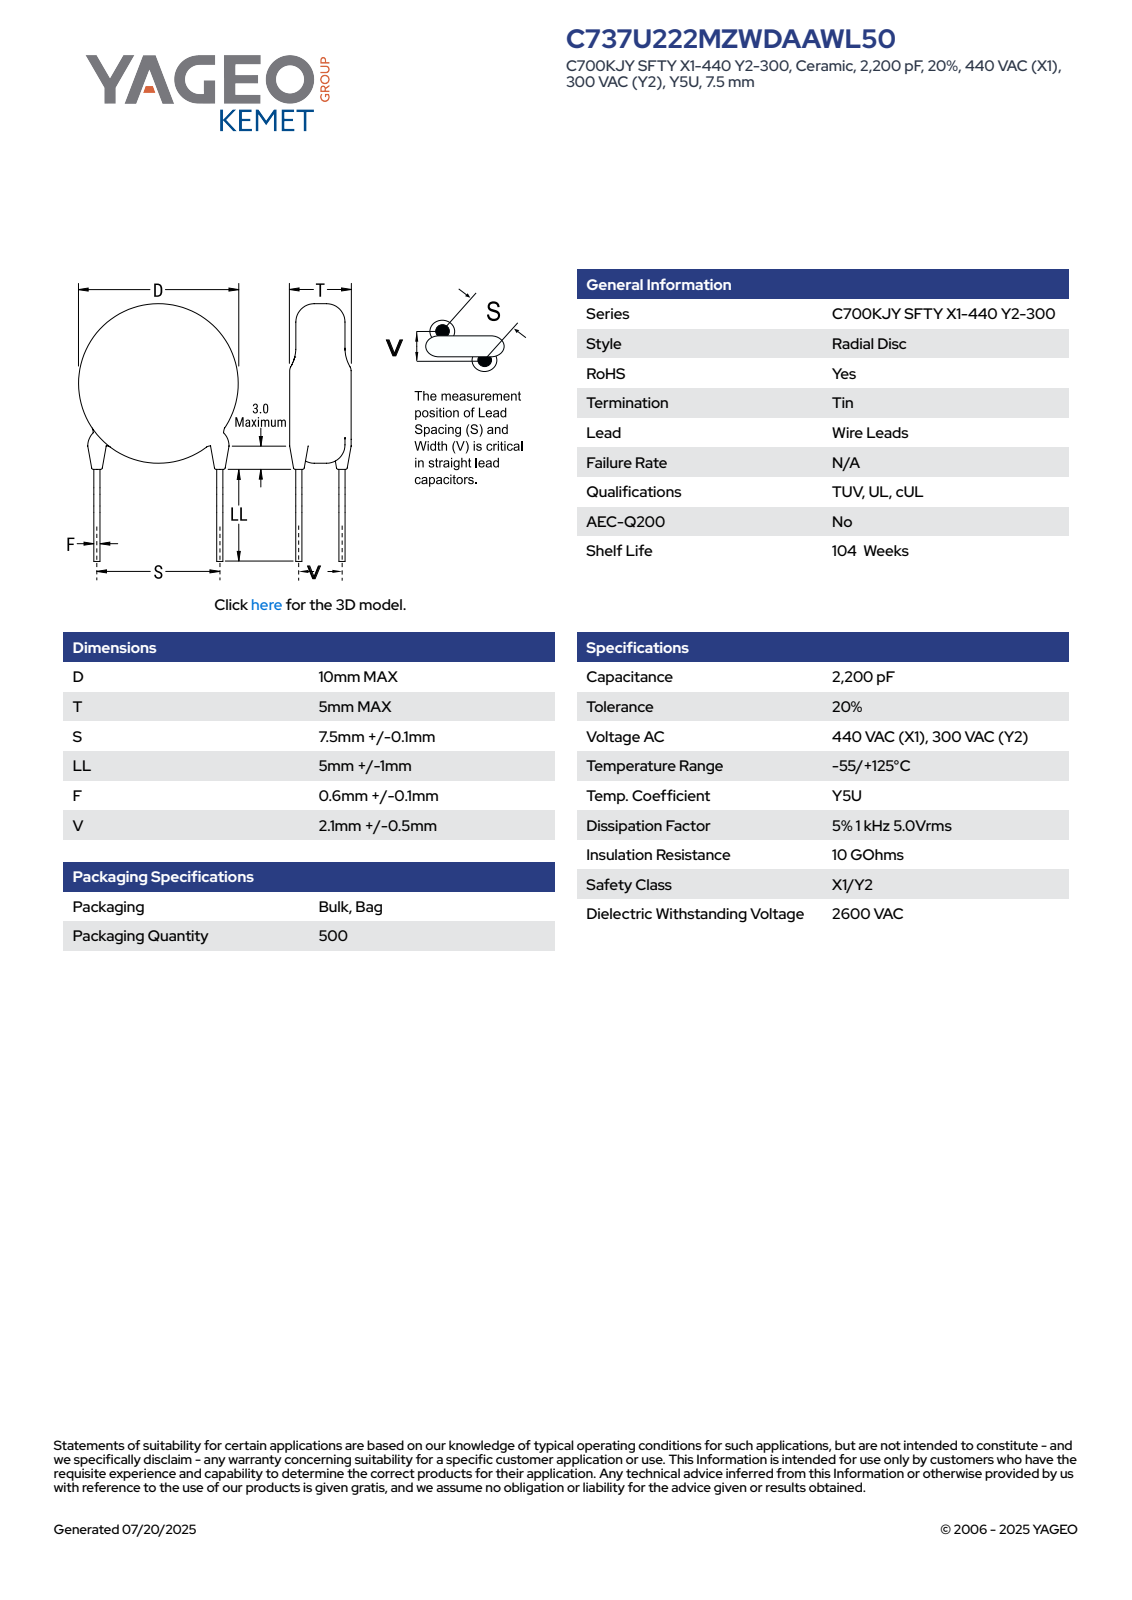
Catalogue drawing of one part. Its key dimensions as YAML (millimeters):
part_name: "CCD_KST_10X5_D10T5S7.6LL6F0.7V2.1"
step_written_by: "SolidWorks 2021 (AUTOMOTIVE_DESIGN)"
units: millimeters
bodies: {solids: 4, faces: 80, planar: 63, cylindrical: 13, other: 4}
overall_size: [17.12, 10, 5]
volume: 391
surface_area: 342
round_bosses_or_shafts:
  - {diameter: 1.2, count: 2}
  - {diameter: 0.7, count: 2}
  - {diameter: 10, count: 1}
partial_cylinders:
  - {radius: 0.6, count: 2}
face_to_face_distances: [5, 6.01, 12.84, 6.83, 11.68, 5.67, 1.16, 0.32, 0.94, 0.51]
